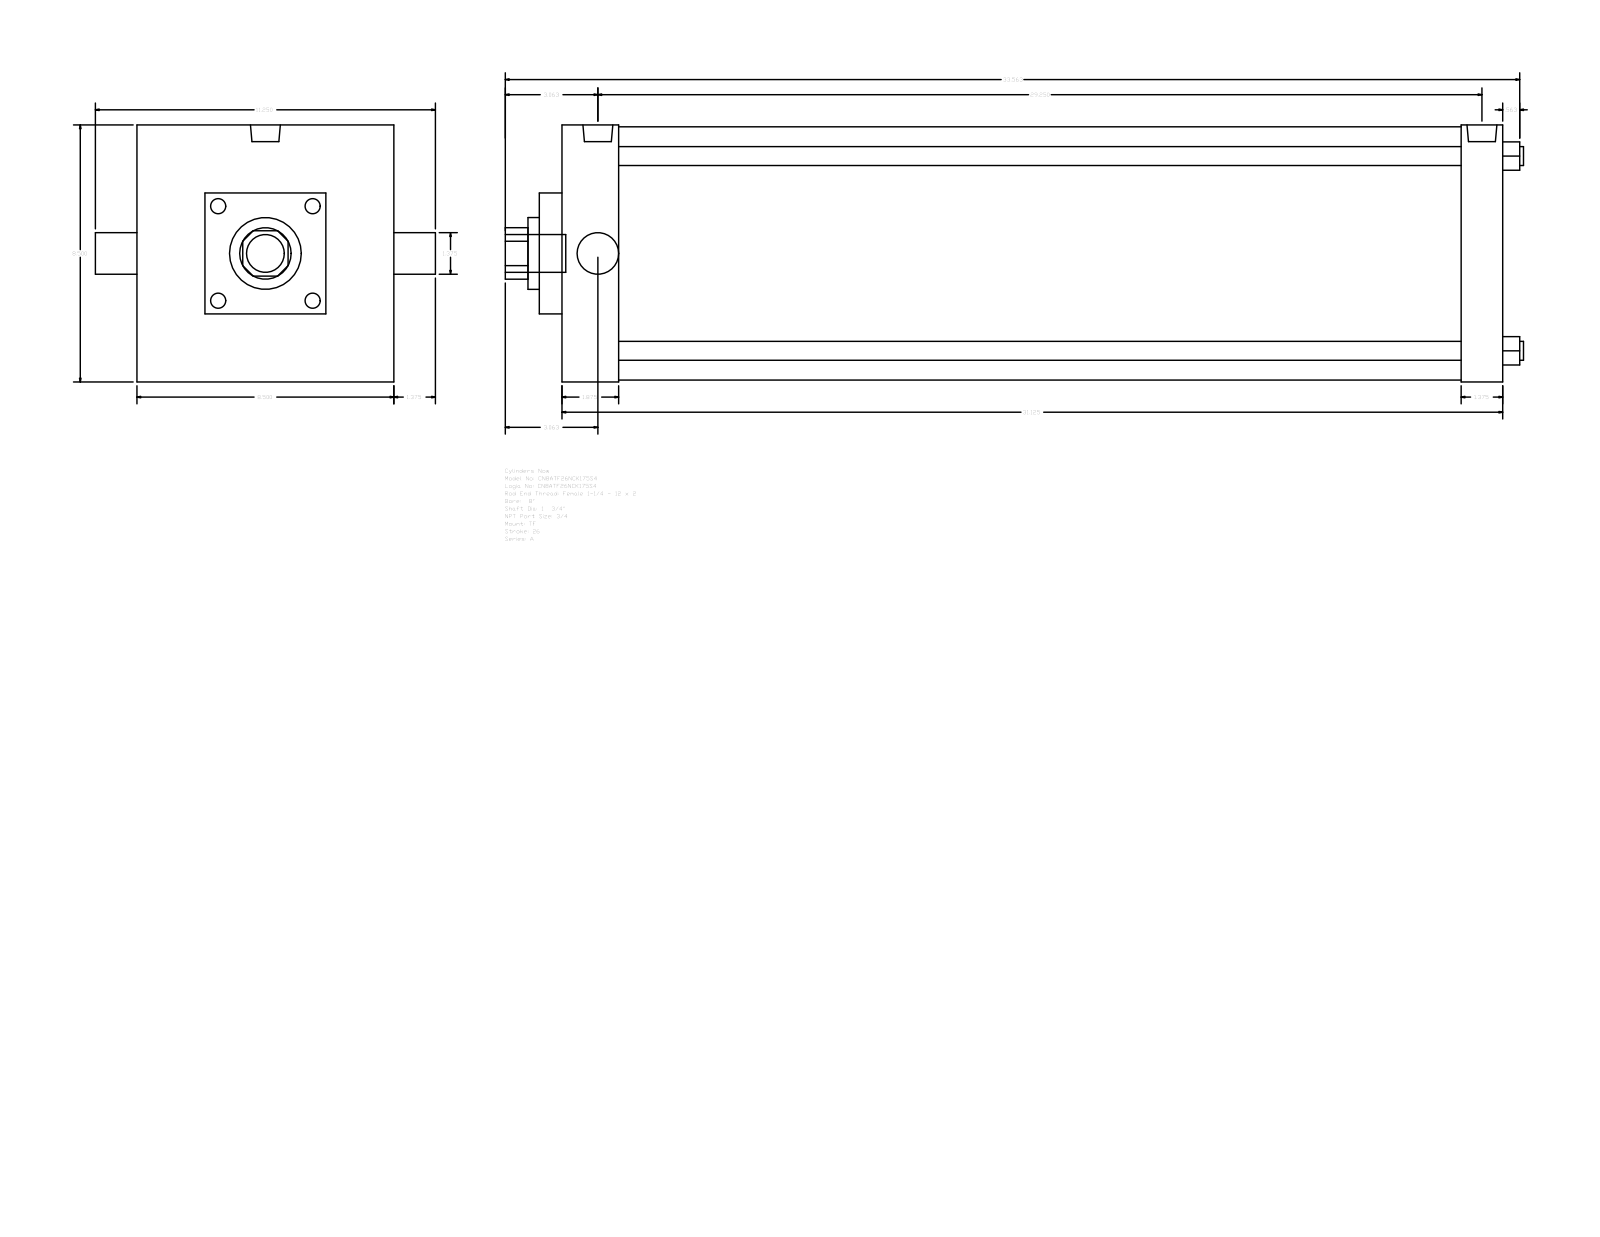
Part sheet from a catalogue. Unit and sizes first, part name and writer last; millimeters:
Units: millimetres
Overall size (bounding box): 855.66 × 285.75 × 215.9
Round holes (diameter × count): ⌀15.88 ×4, ⌀34.92 ×1, ⌀44.45 ×1, ⌀60.33 ×1, ⌀212.72 ×1
Round bosses / shafts (diameter × count): ⌀15.08 ×3, ⌀25.12 ×2, ⌀31.75 ×1
Partial cylindrical surfaces — rounded edges, fillets, slot ends (radius × count): R21.63 ×1
Main face-to-face distances: 790.58, 215.9, 34.93, 47.63, 742.95, 755.65, 708.02, 19.05, 57.15, 158.75
Hole centre spacings: 115.67, 163.58, 231.34
Bodies: 0 solids, 89 faces (65 planar, 24 cylindrical, 0 other)
Part name (STEP PRODUCT): A_TF__0800_1.75
STEP written by: GSSL Pune (CONFIG_CONTROL_DESIGN)
